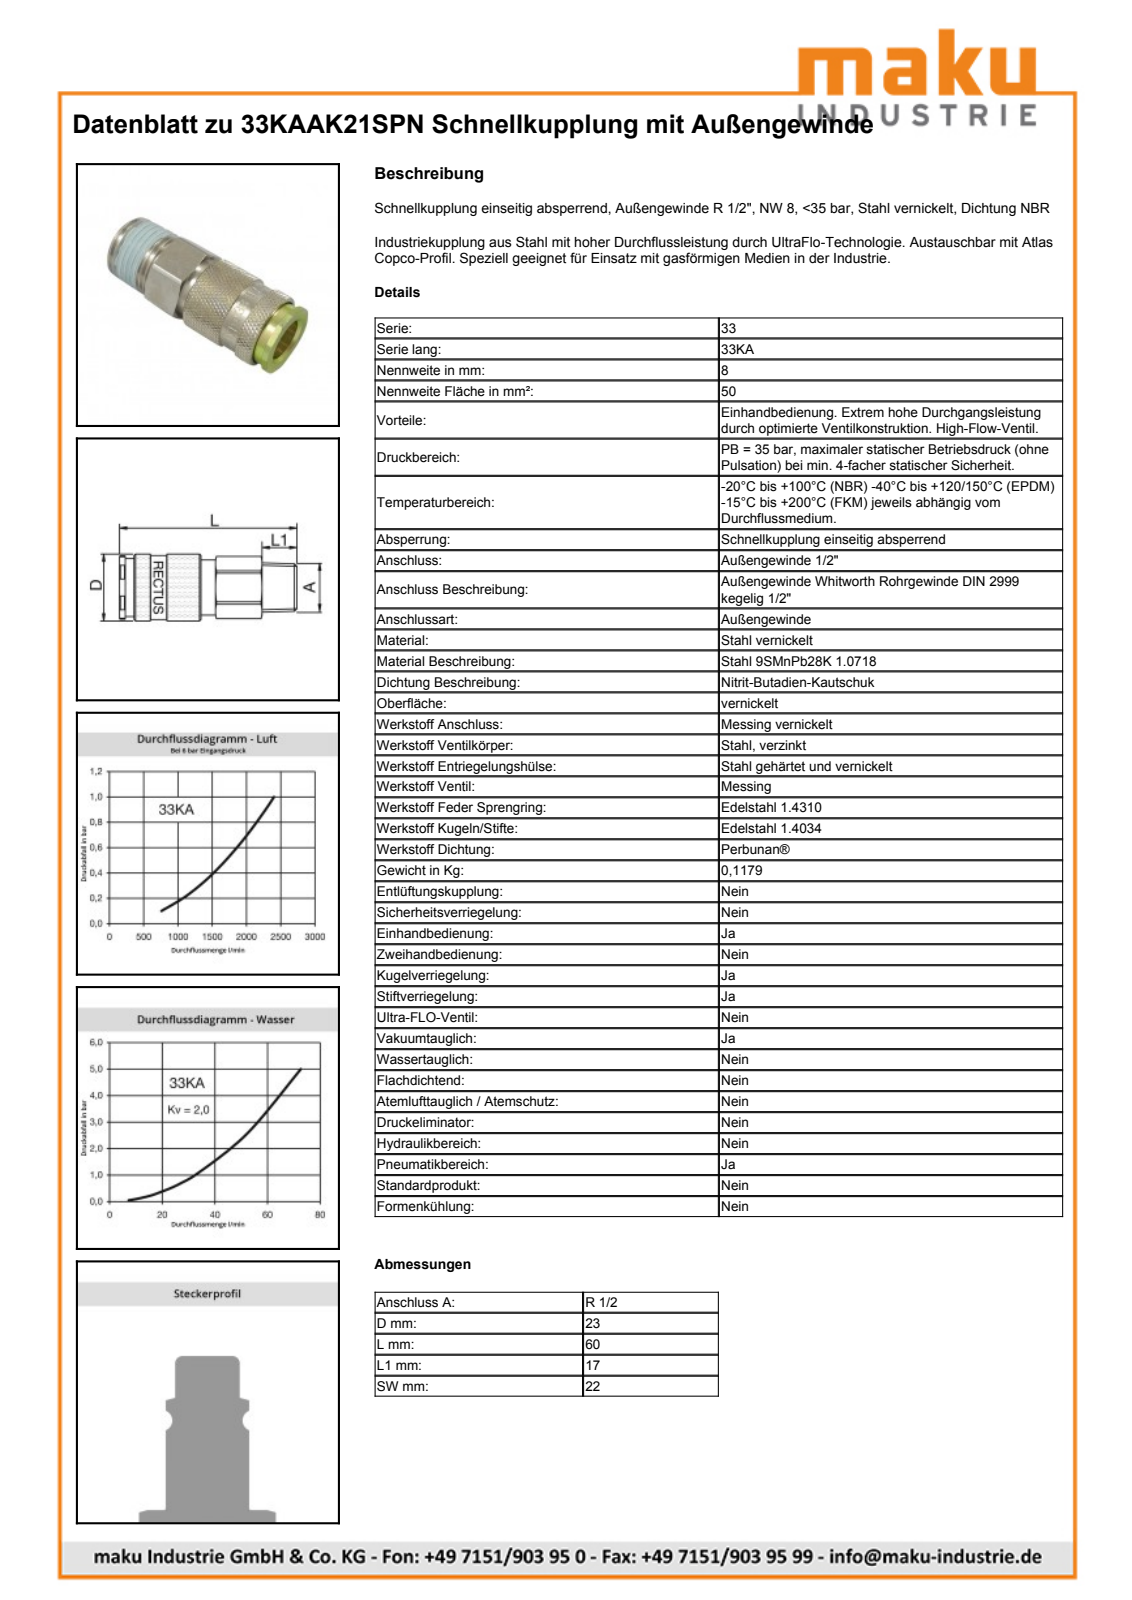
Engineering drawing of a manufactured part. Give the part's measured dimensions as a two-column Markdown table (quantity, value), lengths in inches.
| quantity | value |
| --- | --- |
| part name | D107416 |
| STEP written by | Autodesk Inventor 2013 (AUTOMOTIVE_DESIGN) |
| units | inches |
| bodies | 2 solids, 517 faces (181 planar, 69 cylindrical, 267 other) |
| overall size | 2.402 × 0.965 × 0.939 |
| volume | 1.344 in³ |
| surface area | 13.58 in² |
| round holes (diameter × count) | 0.614 × 1, 0.64 × 1, 0.72 × 1, 0.762 × 1, 0.815 × 1 |
| round bosses / shafts (diameter × count) | 0.906 × 1, 0.866 × 1, 0.858 × 1, 0.783 × 1, 0.746 × 1, 0.699 × 1, 0.63 × 1, 0.611 × 1 |
| partial cylindrical surfaces (radius × count) | 0.488 × 1 |
| main face-to-face distances | 0.866, 2.402, 0.197, 0.787, 0.079, 1.181, 0.984, 0.531, 1.26, 1.142 |
